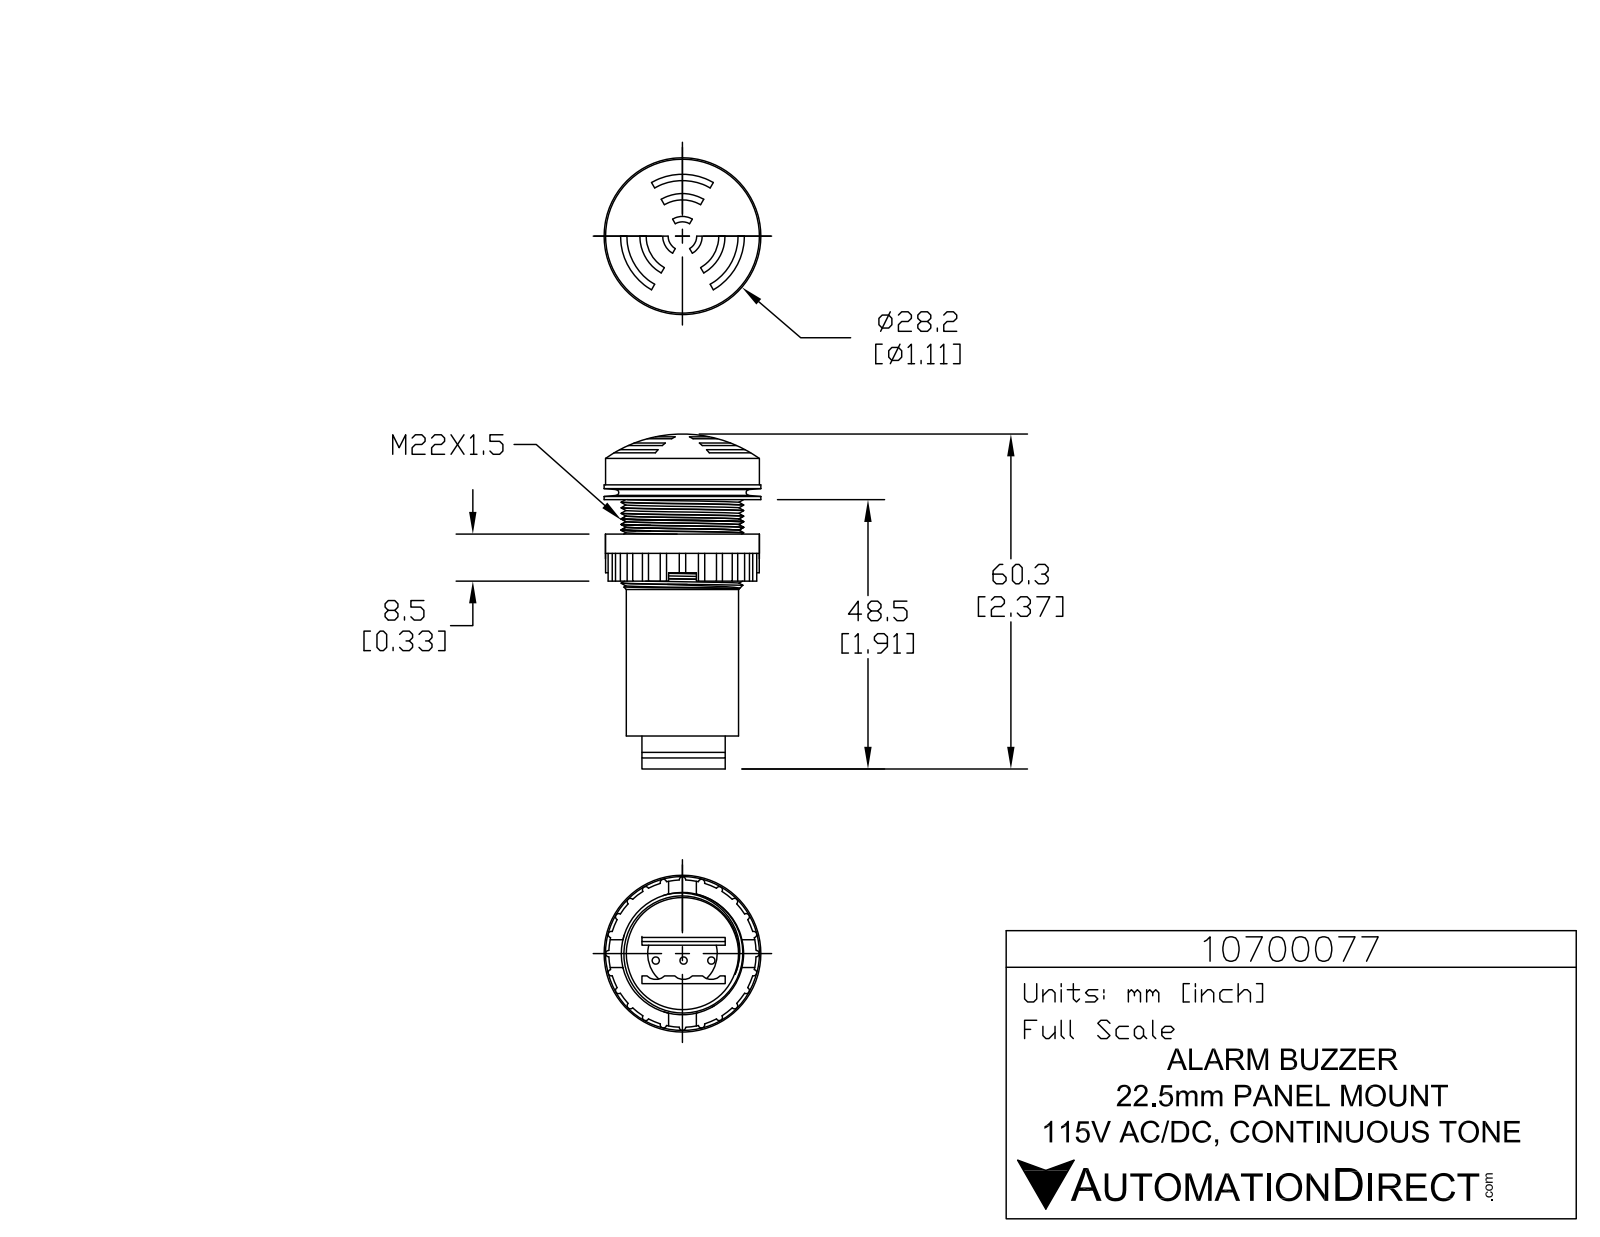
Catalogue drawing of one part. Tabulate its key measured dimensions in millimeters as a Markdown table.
| quantity | value |
| --- | --- |
| part name | 10700077 |
| STEP written by | SolidWorks 2017 (AUTOMOTIVE_DESIGN) |
| units | millimeters |
| bodies | 1 solid, 161 faces (37 planar, 103 cylindrical, 21 other) |
| overall size | 59.4 × 28.2 × 28.2 |
| volume | 21 583 mm³ |
| surface area | 7 928 mm² |
| round bosses / shafts (diameter × count) | 1.3 × 3, 28.2 × 1, 27.7 × 1, 22 × 1, 20.2 × 1 |
| partial cylindrical surfaces (radius × count) | 0.57 × 24, 2.25 × 3, 6.25 × 1, 13.25 × 1 |
| main face-to-face distances | 35.5, 8.5, 27, 6.9, 32.95, 3.5, 41.65, 14.65, 6.15, 2.55 |
